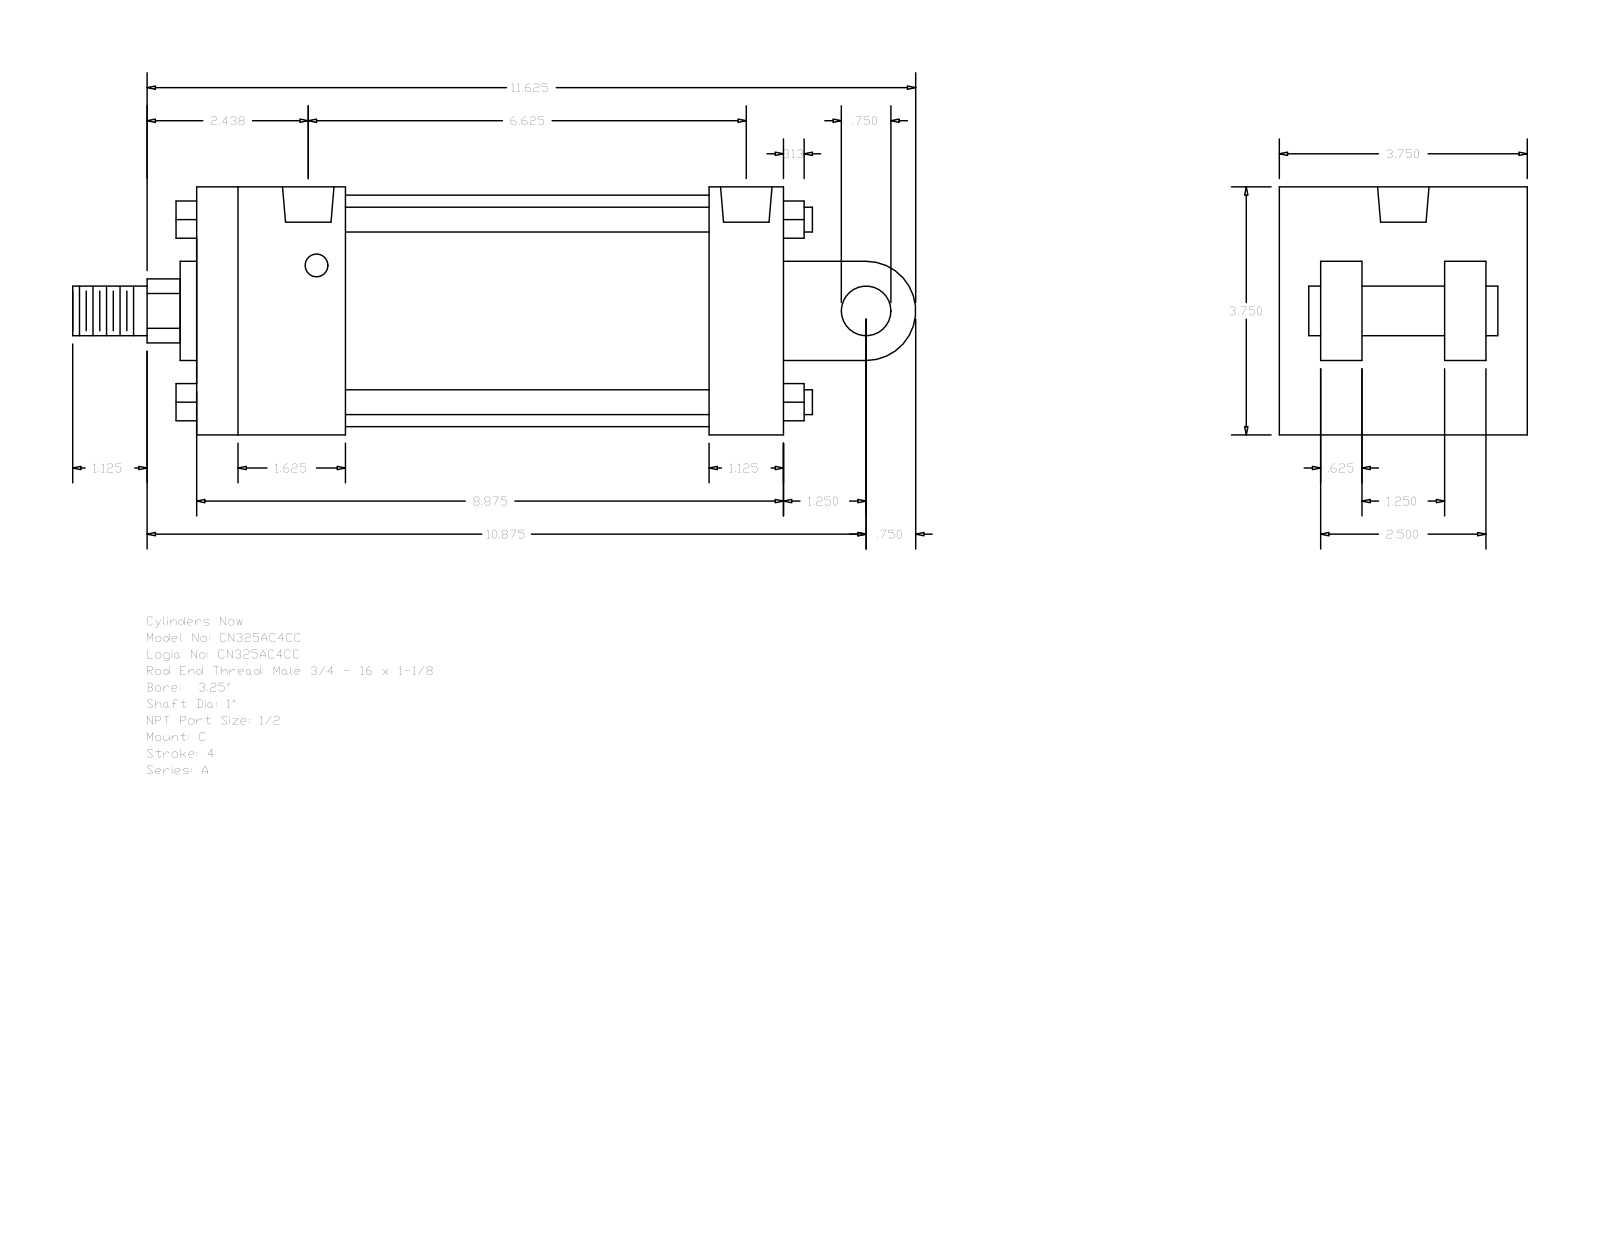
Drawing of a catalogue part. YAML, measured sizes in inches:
part_name: "A_C__0325_1"
step_written_by: "GSSL Pune (CONFIG_CONTROL_DESIGN)"
units: inches
bodies: {solids: 0, faces: 135, planar: 102, cylindrical: 33, other: 0}
overall_size: [12.75, 3.75, 3.75]
round_holes:
  - {diameter: 0.344, count: 4}
  - {diameter: 0.778, count: 2}
round_bosses_or_shafts:
  - {diameter: 0.375, count: 4}
  - {diameter: 0.75, count: 2}
  - {diameter: 3.5, count: 1}
  - {diameter: 1.5, count: 1}
  - {diameter: 1, count: 1}
partial_cylinders:
  - {radius: 0.484, count: 1}
  - {radius: 0.75, count: 1}
face_to_face_distances: [3.75, 8.875, 0.625, 2.5, 1.125, 3.125, 1.25, 1.875, 2.625, 7.75]
hole_center_spacings: [0.125, 6.375, 6.5, 6.625]
